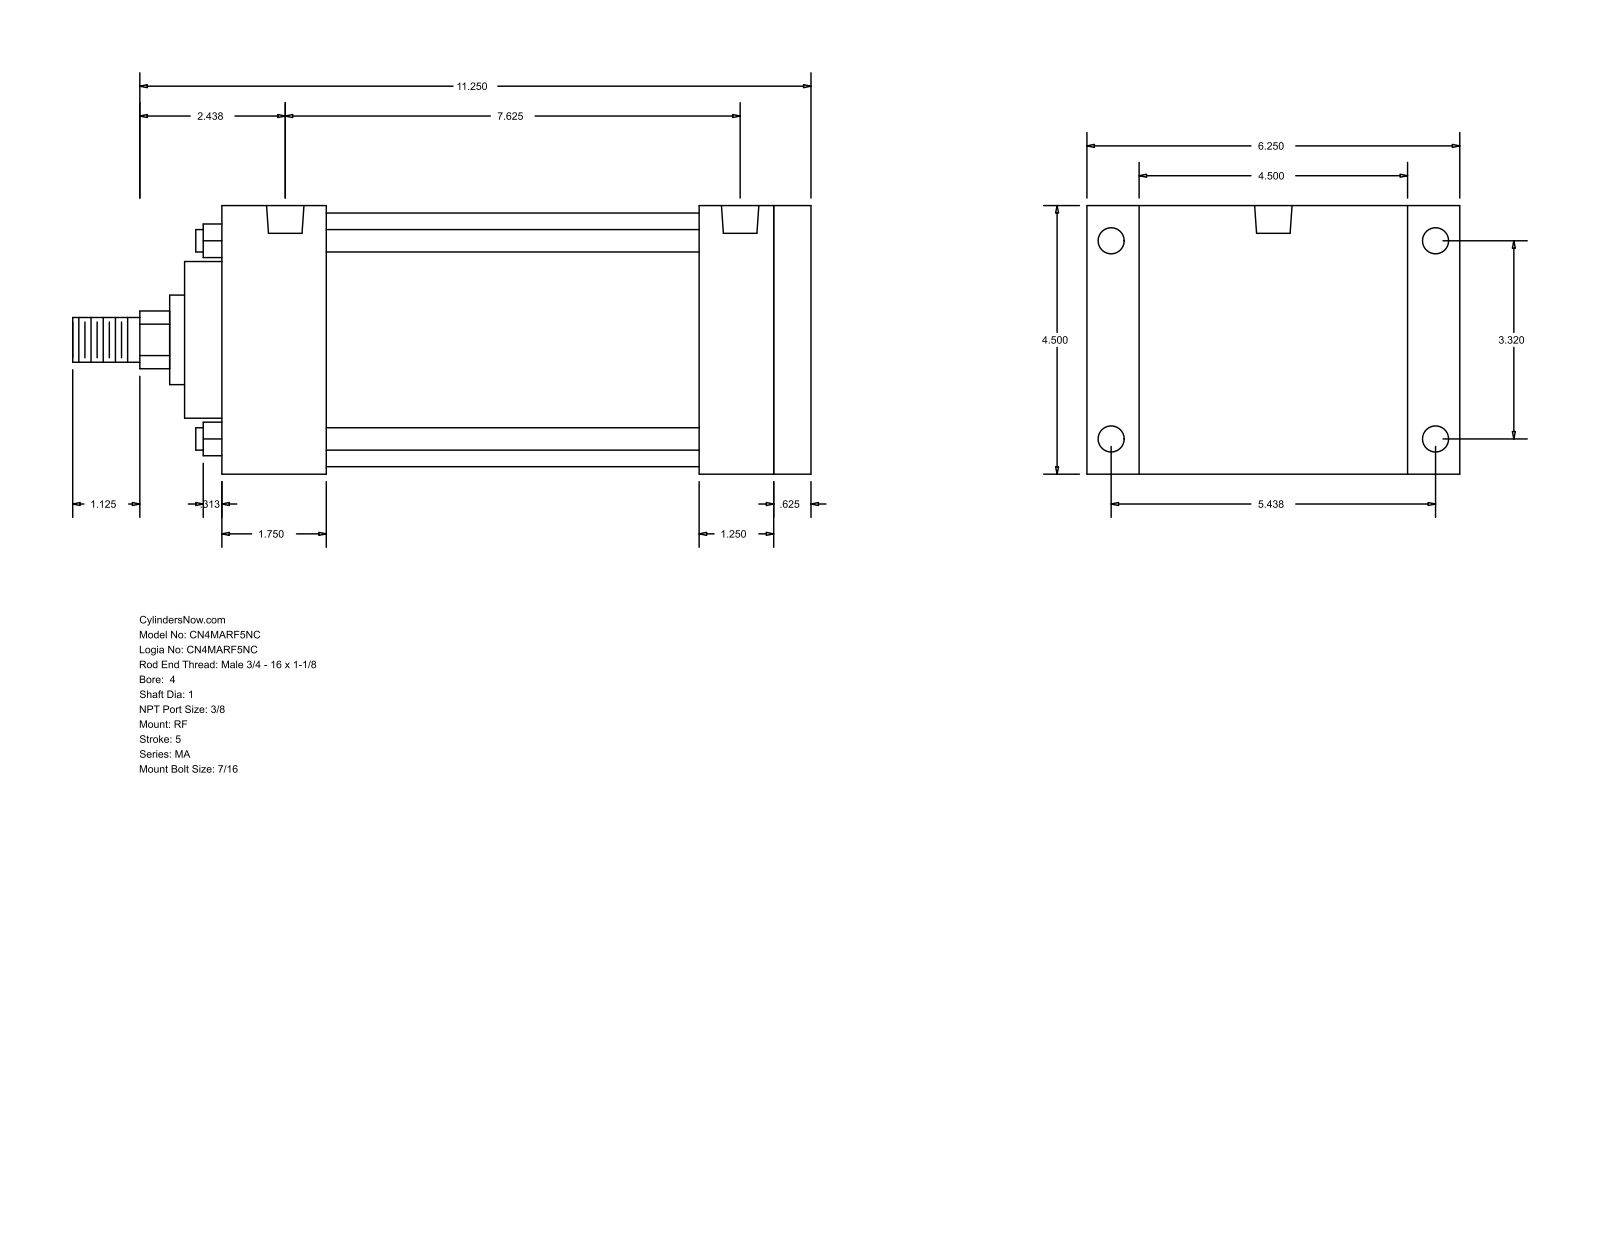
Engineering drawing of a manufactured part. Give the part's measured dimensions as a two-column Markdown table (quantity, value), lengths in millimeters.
| quantity | value |
| --- | --- |
| part name | MA_RF__0400_1 |
| STEP written by | GSSL Pune (CONFIG_CONTROL_DESIGN) |
| units | millimeters |
| bodies | 0 solids, 94 faces (65 planar, 29 cylindrical, 0 other) |
| overall size | 314.32 × 158.75 × 114.3 |
| round holes (diameter × count) | 11.11 × 8, 15.93 × 2 |
| round bosses / shafts (diameter × count) | 9.53 × 4, 107.95 × 1, 66.67 × 1, 38.1 × 1, 25.4 × 1, 19.05 × 1 |
| partial cylindrical surfaces (radius × count) | 12.29 × 1 |
| main face-to-face distances | 114.3, 250.83, 15.87, 234.96, 22.23, 136.53, 203.2, 31.76, 47.63, 44.46 |
| hole center spacings | 84.32, 138.12, 161.82, 184.15, 4.76, 4.77, 188.91, 188.92 |
